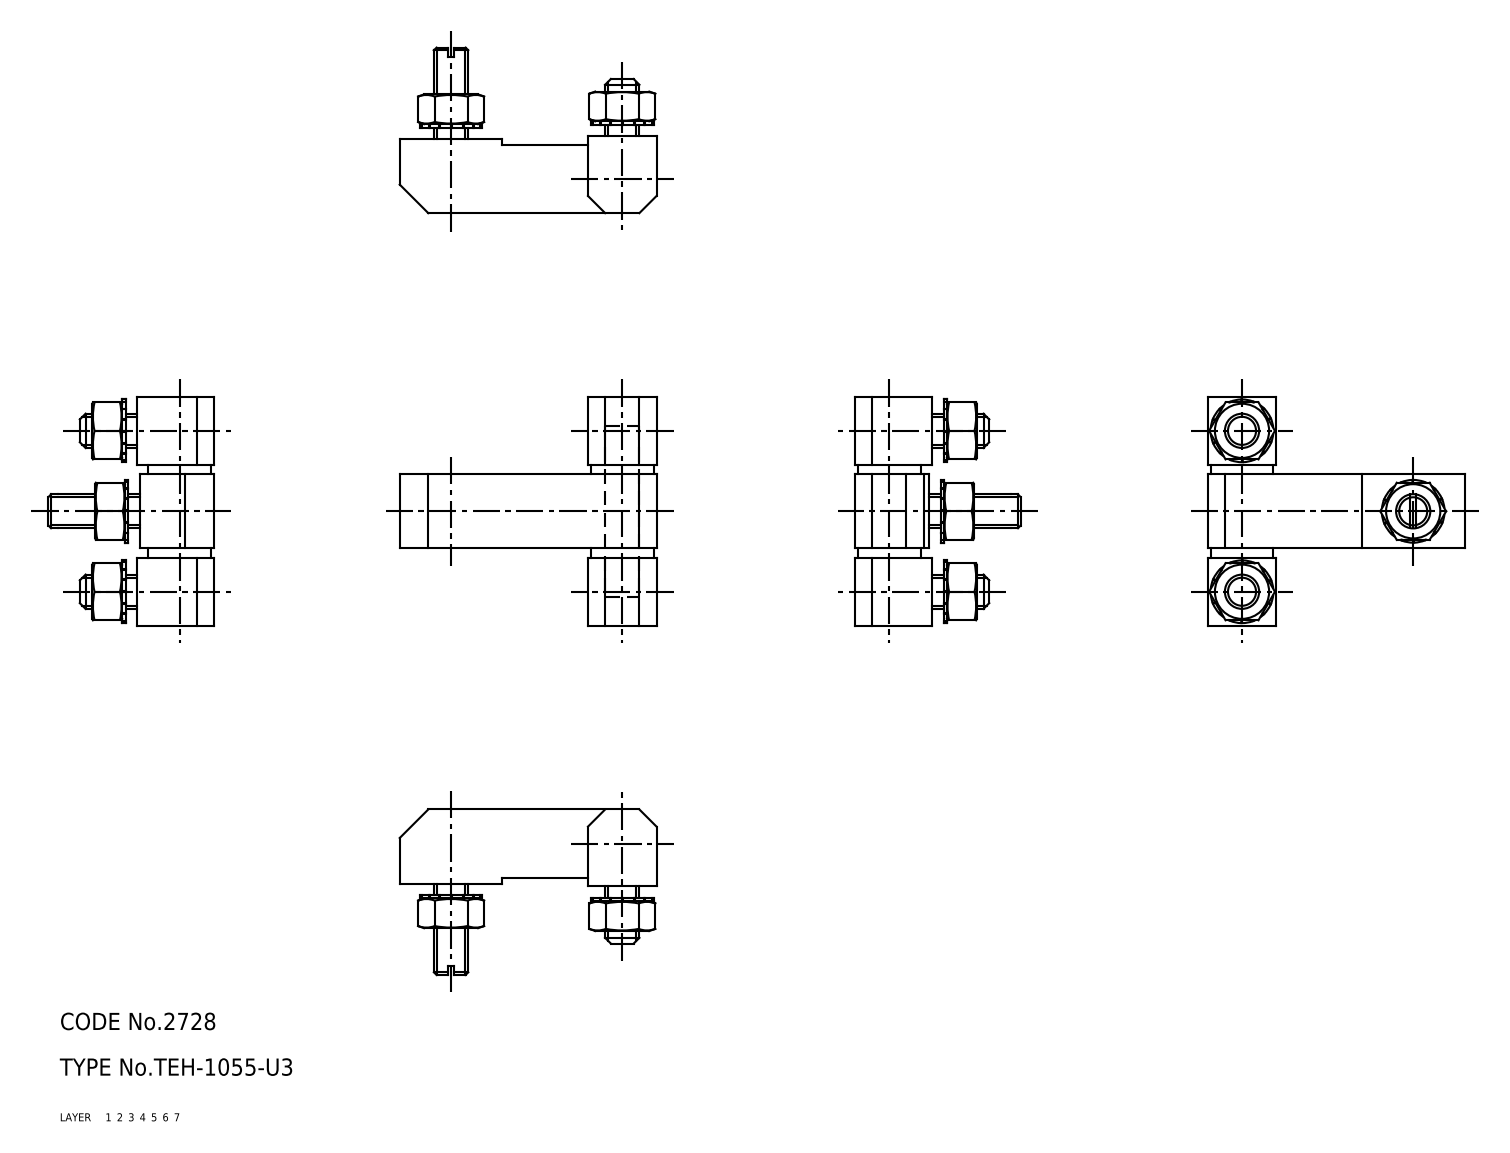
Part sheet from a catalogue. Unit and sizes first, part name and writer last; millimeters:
Units: millimetres
Overall size (bounding box): 45 × 40.2 × 29
Volume: 12 857 mm³ · Surface area: 8 104 mm²
Bodies: 12 solids, 130 faces (0 planar, 0 cylindrical, 130 other)
Part name (STEP PRODUCT): washer_B; nut; washer_A; hinge pieces_A (+3 more)
STEP written by: CADfix (AUTOMOTIVE_DESIGN)
